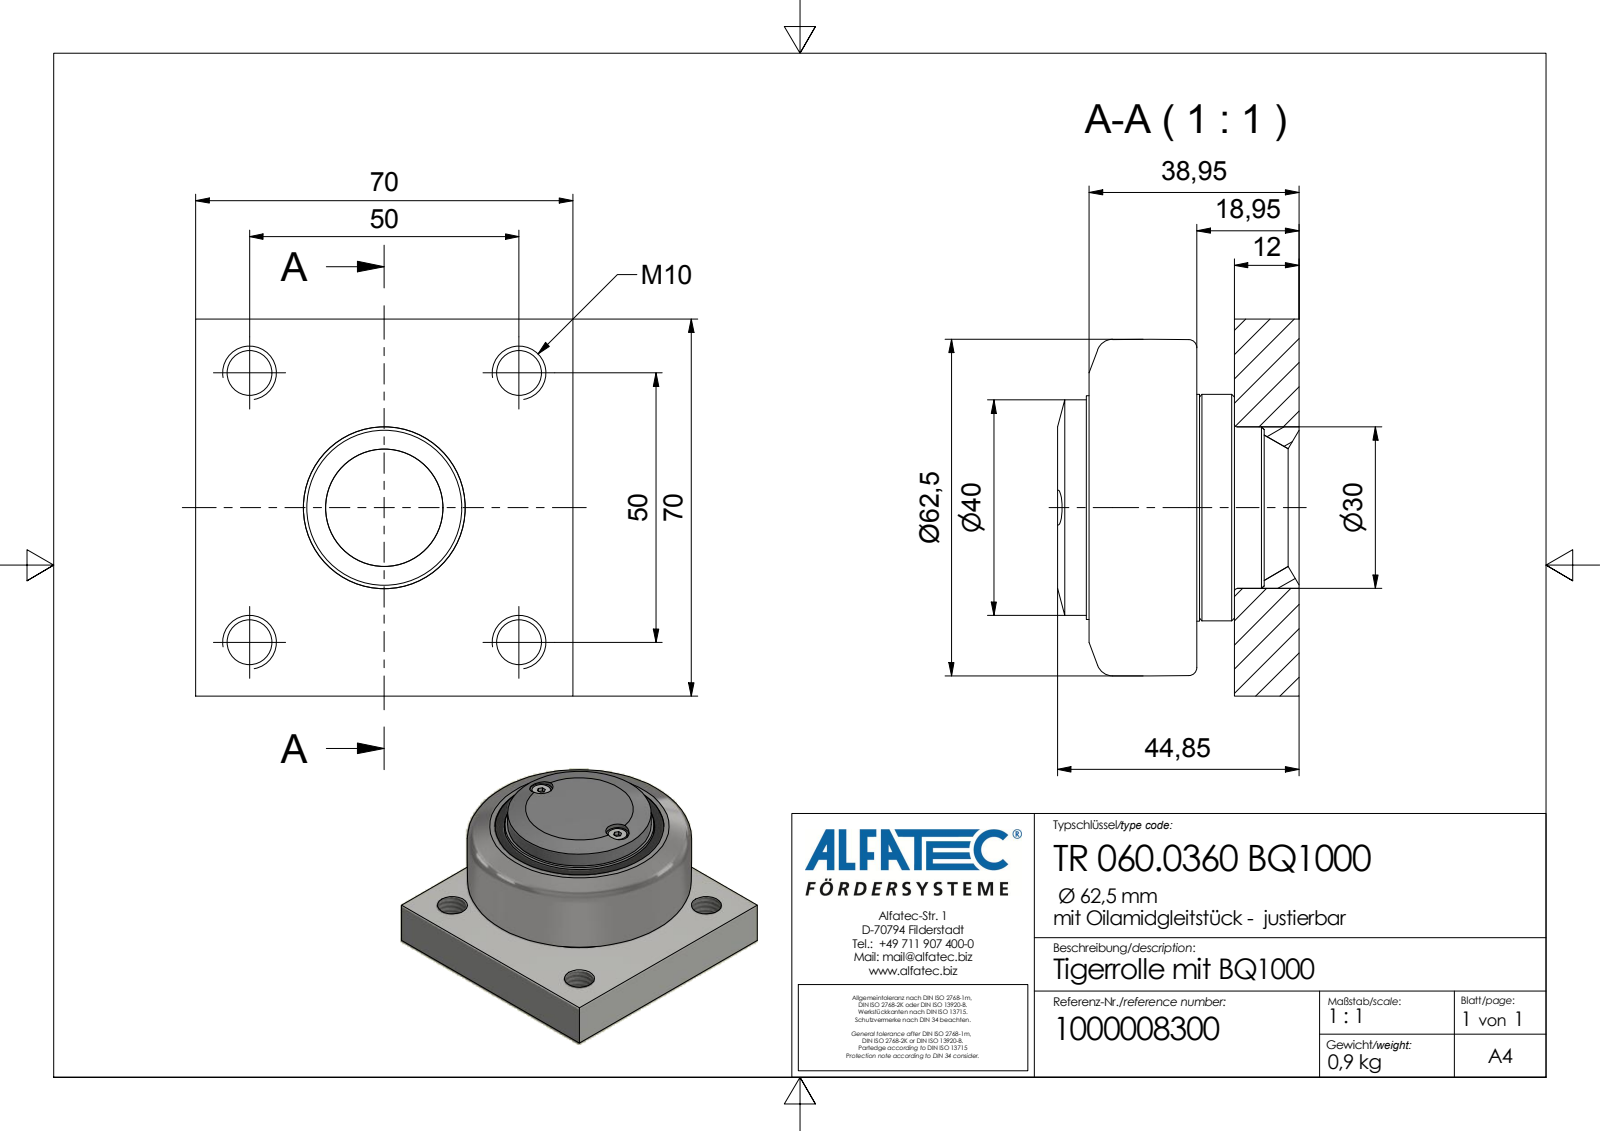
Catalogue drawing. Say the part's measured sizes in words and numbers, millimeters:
The part is named "TR 060.0360 BQ1000_Kontur". Its 3-D file was written by "Autodesk Inventor 2020 (AP242_MANAGED_MODEL_BASED_3D_ENGINEERING_MIM_LF)". It is 1 solid with 61 faces: 32 planar, 17 cylindrical and 12 other. Overall it measures 70 by 70 by 45 millimeters. Its volume is 131 202 cubic millimeters and its surface area 23 141 square millimeters. Round holes: 4 of diameter 8.38, 2 of diameter 6.5, 1 of diameter 30, 1 of diameter 42, 1 of diameter 42.97, 1 of diameter 47. Round bosses or shafts: 2 of diameter 5.35, 1 of diameter 42.1, 1 of diameter 41.5, 1 of diameter 40. The main face-to-face distances are 12, 70, 6.95, 18.95, 26.05, 45, 33, 38.95, 26.95, 20. The hole center spacings are 26.93, 35.36, 47.17, 50, 15, 70.71, 30.
